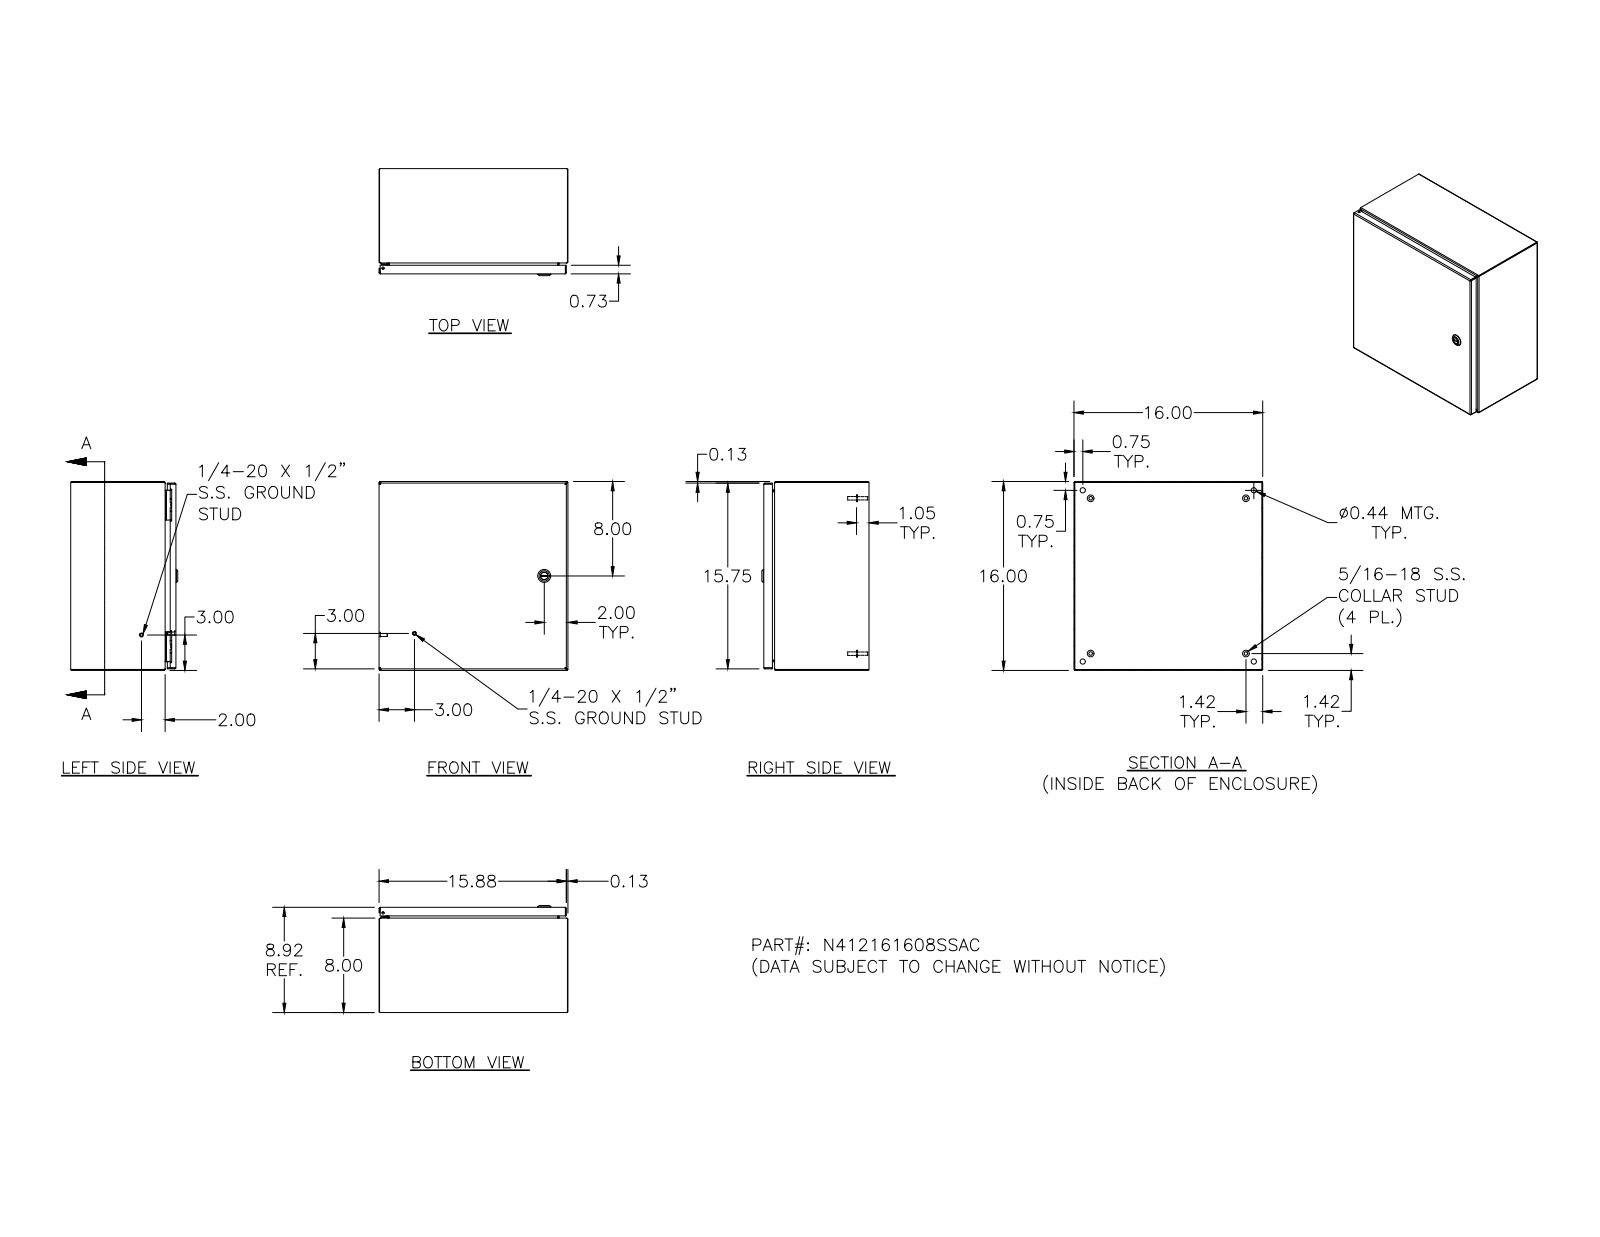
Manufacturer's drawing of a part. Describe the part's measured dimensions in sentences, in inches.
The part is named "N412161608SSAC; NA12161608SSACBKP; 388151; N4121616SSACLID (+8 more)". Its 3-D file was written by "Autodesk Inventor 2011 (AUTOMOTIVE_DESIGN)". It is 34 solids with 1364 faces: 523 planar, 497 cylindrical and 344 other. Overall it measures 16 by 16 by 9.075 inches. Its volume is 85.82 cubic inches and its surface area 2 336 square inches. Round holes: 5 of diameter 0.188, 4 of diameter 0.093, 4 of diameter 0.152, 4 of diameter 0.167, 4 of diameter 0.172, 4 of diameter 0.437, 2 of diameter 0.156, 1 of diameter 0.187, 1 of diameter 0.197, 1 of diameter 0.315, 1 of diameter 0.394, 1 of diameter 0.402. Round bosses or shafts: 10 of diameter 0.25, 4 of diameter 0.563, 4 of diameter 0.36, 4 of diameter 0.32, 4 of diameter 0.3, 4 of diameter 0.275, 4 of diameter 0.256, 4 of diameter 0.164. Partial cylindrical surfaces (rounded edges, fillets, slot ends): 26 of radius 0.05, 18 of radius 0.016, 16 of radius 0.016, 16 of radius 0.09, 14 of radius 0.031, 14 of radius 0.125, 9 of radius 0.02, 8 of radius 0.032. The main face-to-face distances are 0.074, 15.926, 8.843, 16, 15.852, 8.769, 8.917, 7.926, 0.917, 0.739. The hole center spacings are 12, 0.017, 0.66, 14.5, 0.019, 0.5, 0.648, 0.652.
